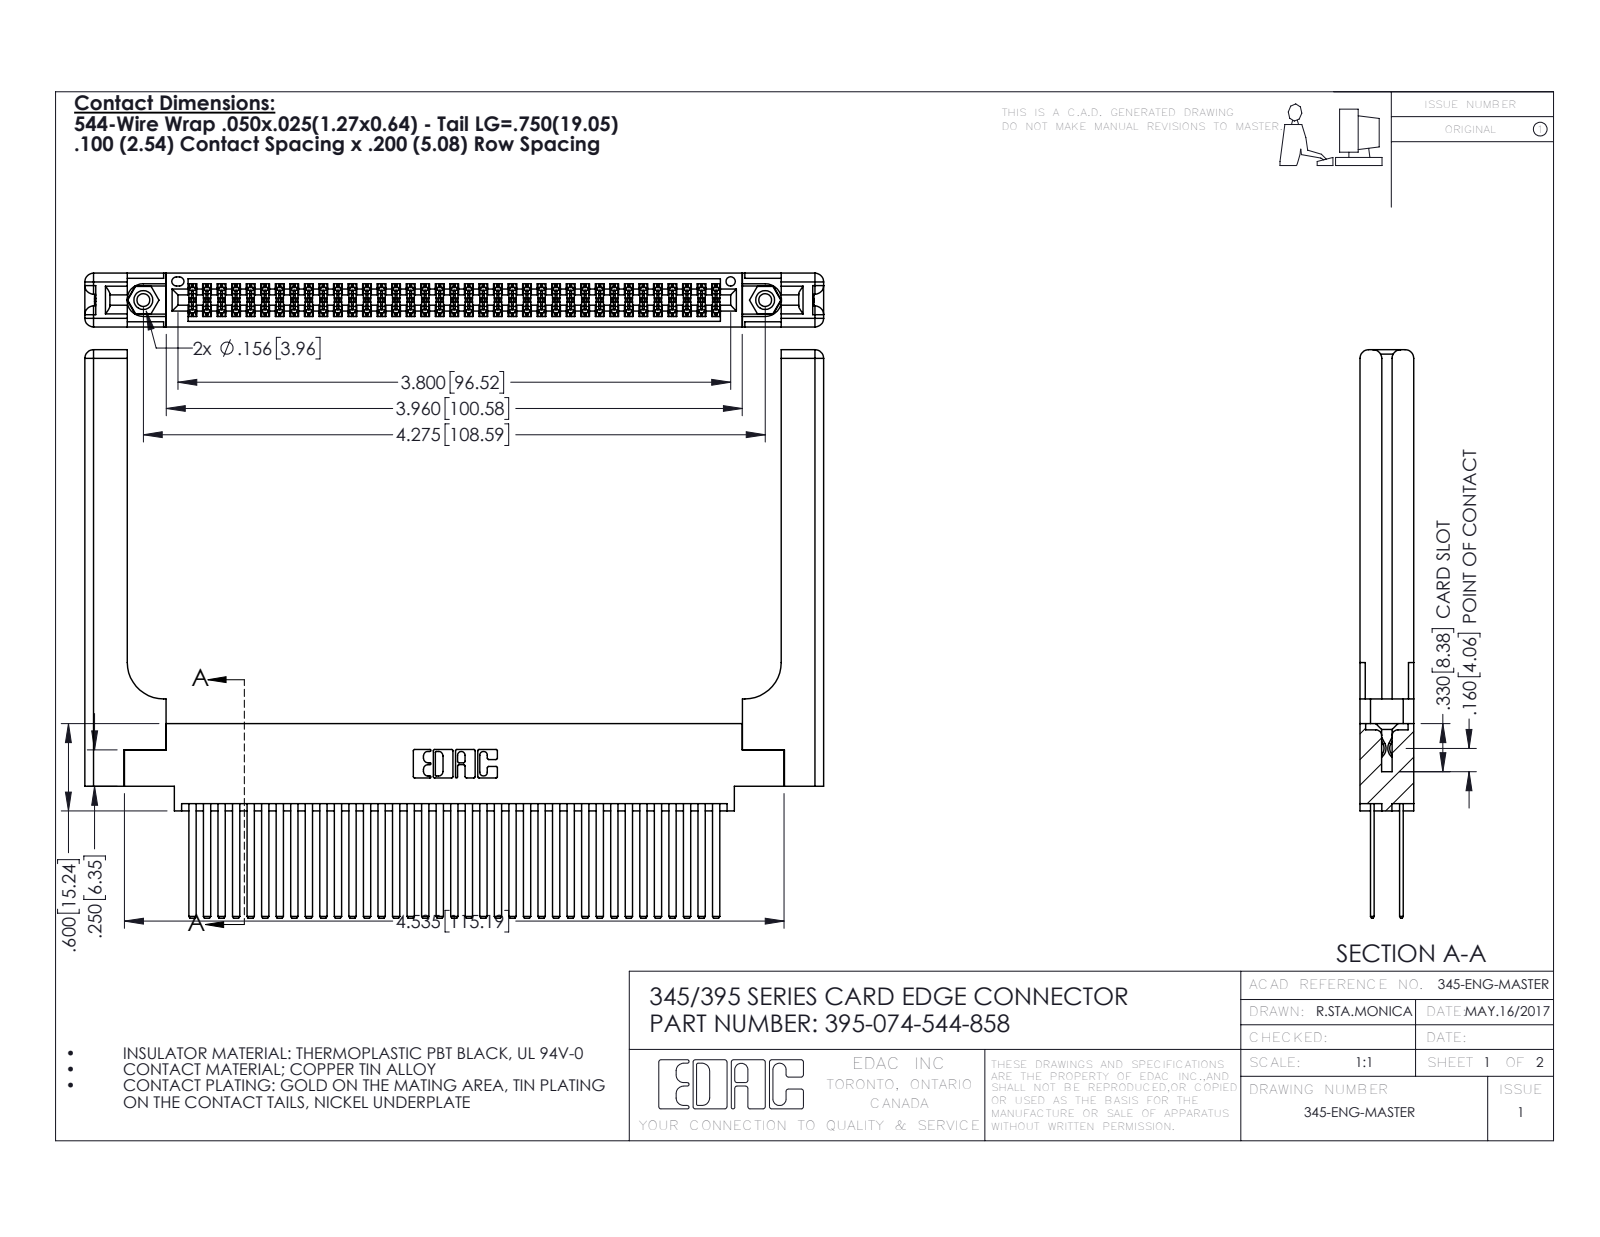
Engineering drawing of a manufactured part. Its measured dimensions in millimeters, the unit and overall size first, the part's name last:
Units: millimetres
Overall size (bounding box): 129 × 99.2 × 9.4
Round holes (diameter × count): ⌀2.3 ×2, ⌀3.2 ×2, ⌀4 ×2, ⌀1.6 ×1
Round bosses / shafts (diameter × count): ⌀3.9 ×2
Partial cylindrical surfaces — rounded edges, fillets, slot ends (radius × count): R0.2 ×111, R0.3 ×22, R1.5 ×16, R0.2 ×6, R0.8 ×6, R0.7 ×3, R0.4 ×2, R0.5 ×2
Main face-to-face distances: 1.8, 7.6, 2.5, 6.9, 0.6, 5.1, 9.4, 5.7, 4.4, 3.8
Hole centre spacings: 6.9, 102.6, 108.6
Volume: 21 880 mm³ · Surface area: 27 970 mm²
Bodies: 79 solids, 3642 faces (2378 planar, 1204 cylindrical, 60 other)
Part name (STEP PRODUCT): 345-292-001_345-293-144; 345-250-001_345-250-001-102; 345-220-058_345-220-058; 395-074-544-858 (+1 more)
STEP written by: SolidWorks 2016 (CONFIG_CONTROL_DESIGN)
